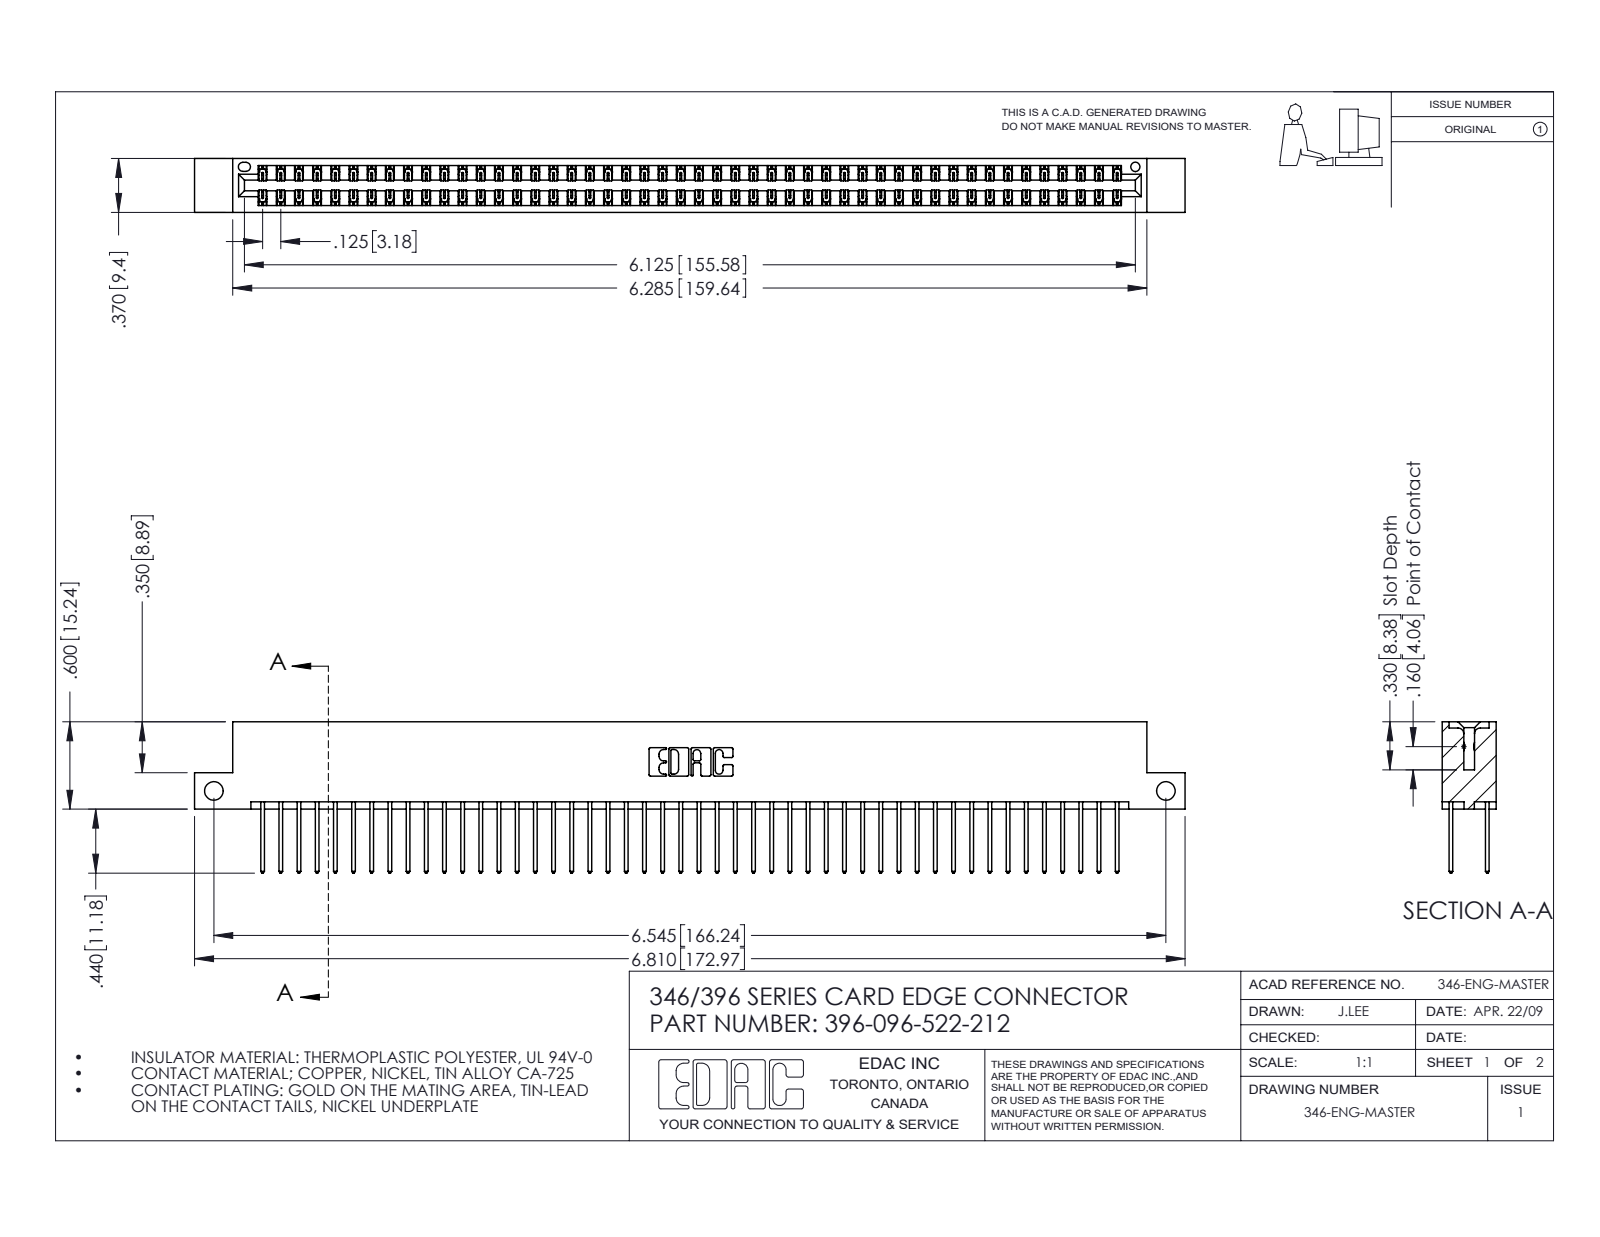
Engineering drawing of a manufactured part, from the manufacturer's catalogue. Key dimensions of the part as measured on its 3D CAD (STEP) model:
Part name (STEP PRODUCT): 396-096-522-212; 346 Part_Flush Mounting Lugs - Side Mount; 345-292-001_345-293-122
STEP written by: SolidWorks 2016 (CONFIG_CONTROL_DESIGN)
Units: inches
Bodies: 97 solids, 5114 faces (3436 planar, 1678 cylindrical, 0 other)
Overall size (bounding box): 6.81 × 1.04 × 0.37
Volume: 1.042 in³ · Surface area: 38.07 in²
Round holes (diameter × count): ⌀0.128 ×2, ⌀0.064 ×1
Partial cylindrical surfaces — rounded edges, fillets, slot ends (radius × count): R0.006 ×144, R0.01 ×96, R0.01 ×22, R0.007 ×6, R0.031 ×6, R0.026 ×3, R0.014 ×2, R0.022 ×2
Main face-to-face distances: 0.048, 0.322, 0.25, 0.072, 0.298, 0.025, 0.37, 0.275, 0.148, 0.222
Hole centre spacings: 6.545
